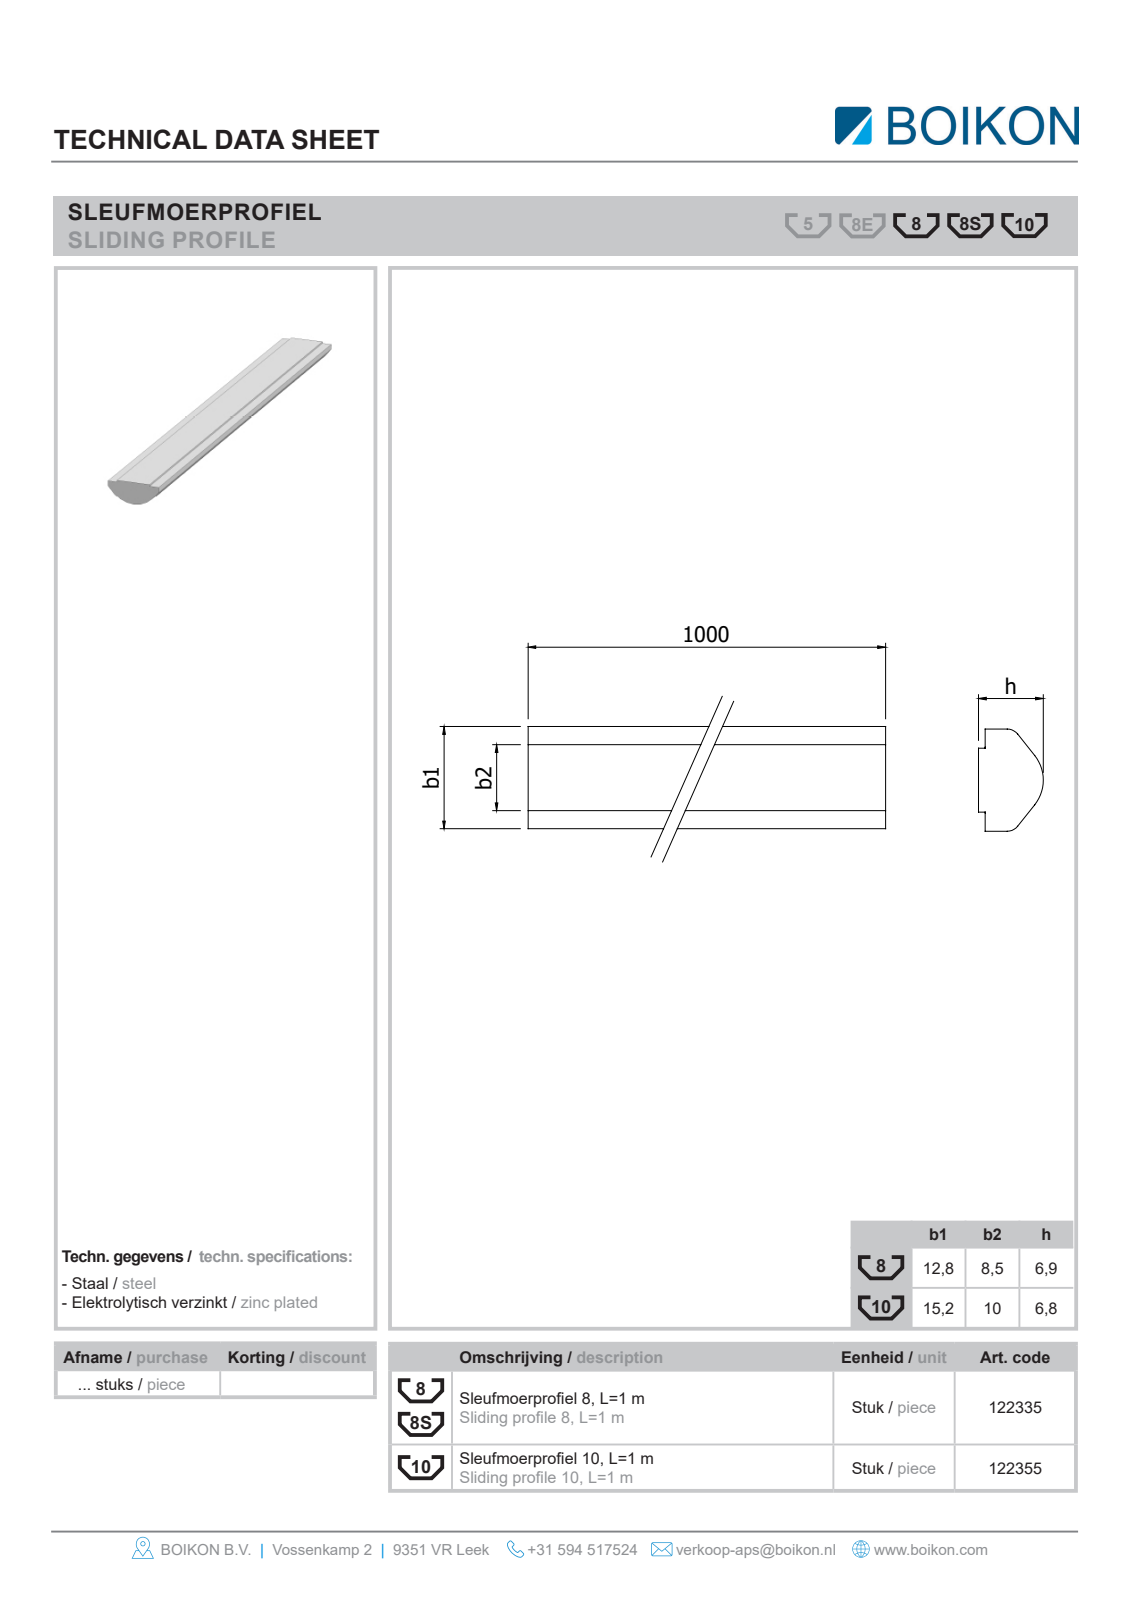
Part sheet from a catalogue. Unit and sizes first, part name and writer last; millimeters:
Units: millimetres
Overall size (bounding box): 1000 × 13 × 7
Partial cylindrical surfaces — rounded edges, fillets, slot ends (radius × count): R0.5 ×2, R2 ×2, R5 ×1
Main face-to-face distances: 0.5, 2.55, 10.45, 7.9, 13, 1000
Volume: 62 020 mm³ · Surface area: 33 731 mm²
Bodies: 1 solid, 16 faces (11 planar, 5 cylindrical, 0 other)
Part name (STEP PRODUCT): Root; 122335Sleufmoerprofiel 8 L= 1mBOIKON0
STEP written by: HiCAD 2013 1802.4 Build 509 (AUTOMOTIVE_DESIGN)
